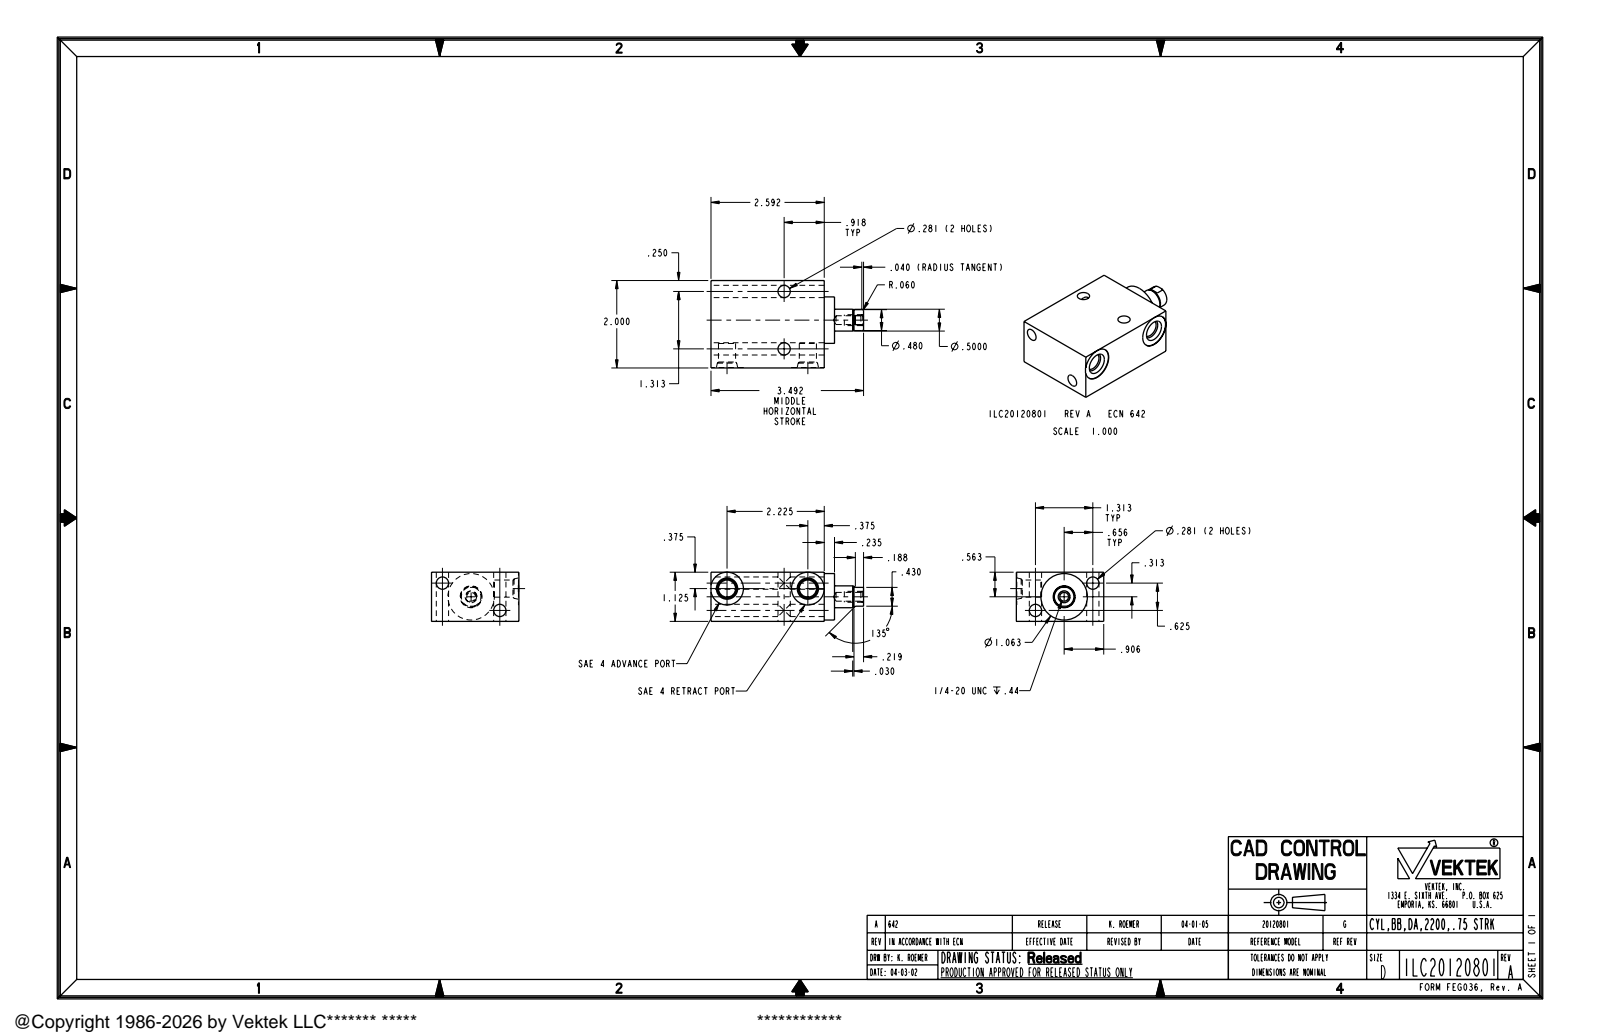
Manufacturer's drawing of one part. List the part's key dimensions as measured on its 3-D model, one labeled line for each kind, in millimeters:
Part name (STEP PRODUCT): ILC20120801
STEP written by: PRO/ENGINEER BY PARAMETRIC TECHNOLOGY CORPORATION, 2004290 (AUTOMOTIVE_DESIGN_CC2)
Units: millimetres
Bodies: 1 solid, 68 faces (19 planar, 33 cylindrical, 16 other)
Overall size (bounding box): 88.7 × 50.8 × 28.6
Volume: 91 130 mm³ · Surface area: 19 360 mm²
Round holes (diameter × count): ⌀7.1 ×4, ⌀10 ×2, ⌀19.1 ×2, ⌀5.1 ×1
Round bosses / shafts (diameter × count): ⌀27 ×1, ⌀12.7 ×1, ⌀12.2 ×1, ⌀6.4 ×1
Main face-to-face distances: 28.6, 50.8, 65.8, 6, 71.8, 50.5, 14.2, 14, 36.6, 16.9
Hole centre spacings: 18.5, 18.5, 33.4, 36.9, 47
